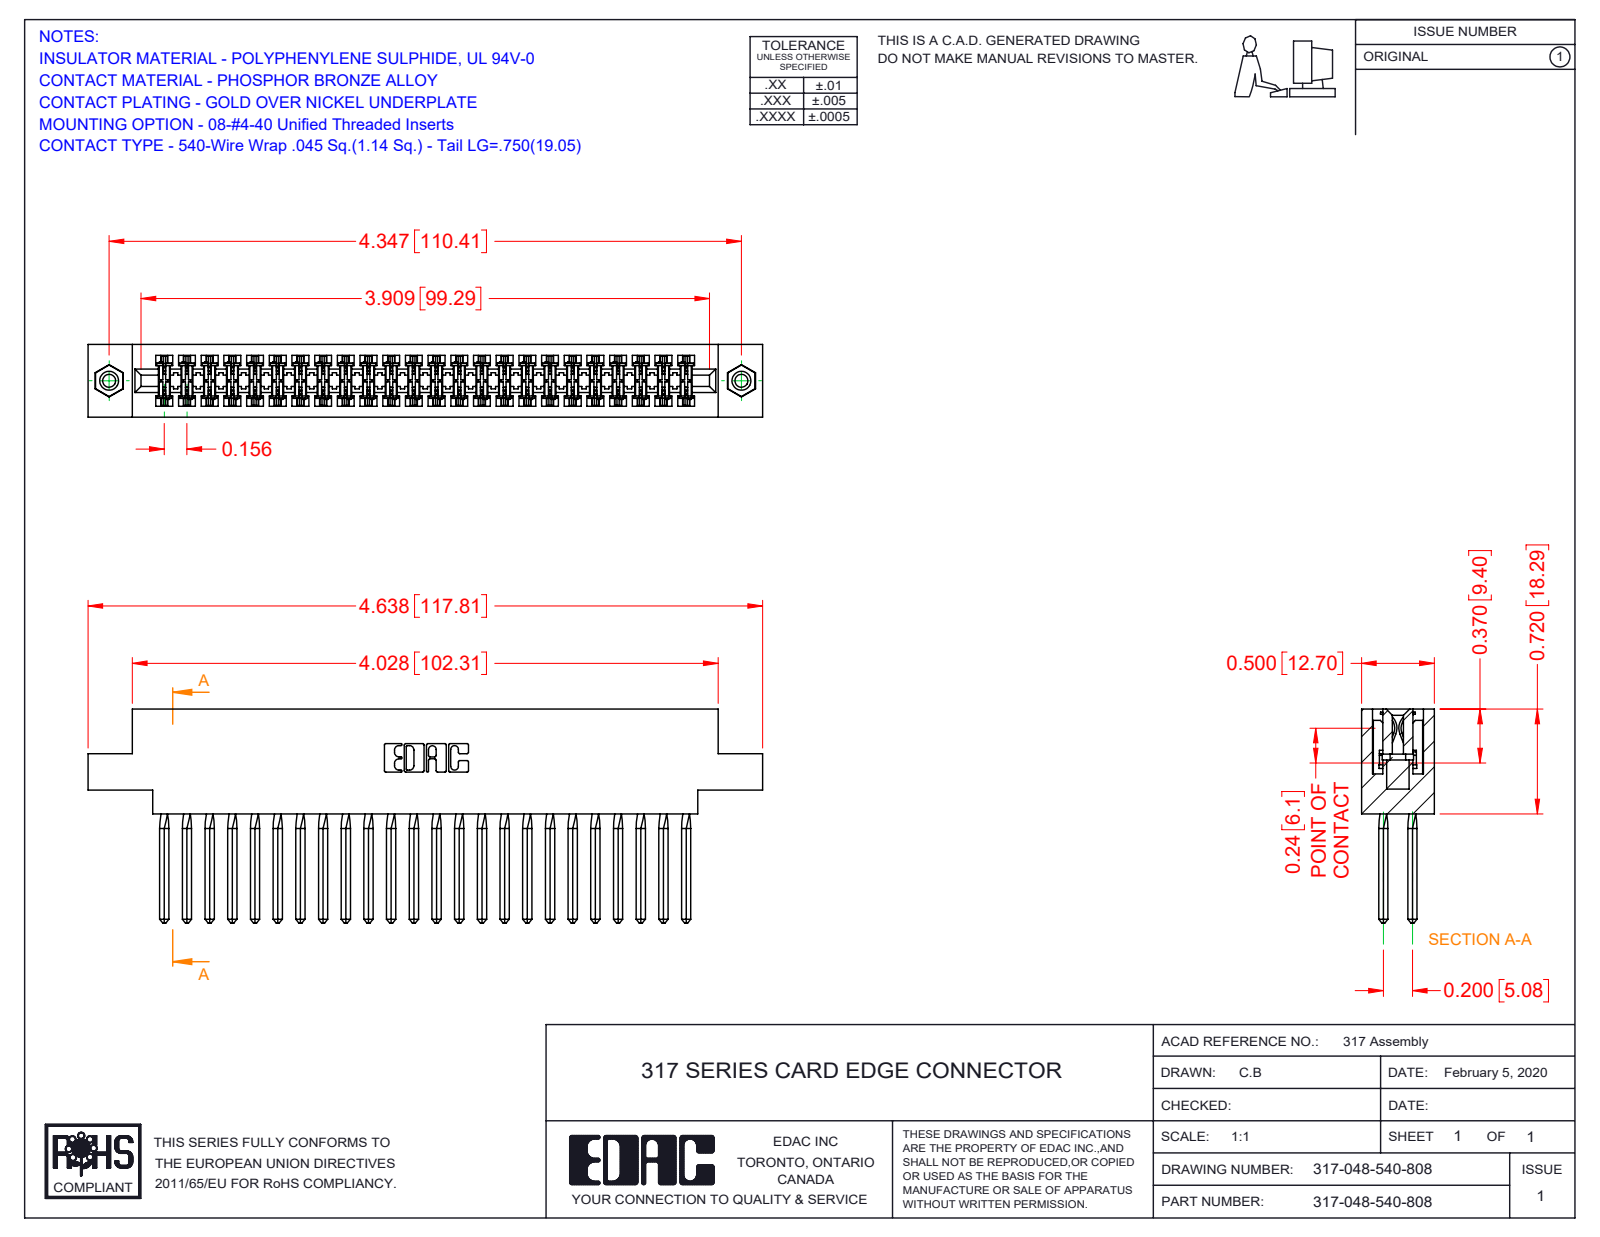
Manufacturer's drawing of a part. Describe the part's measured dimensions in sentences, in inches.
The part is named "317-290-001_540; 345-250-001_345-250-003-102; 317 Part_.156 Dia - TI; 317-048-540-878". Its 3-D file was written by "SolidWorks 2016 (CONFIG_CONTROL_DESIGN)". It is 51 solids with 4434 faces: 3594 planar, 632 cylindrical and 208 other. Overall it measures 4.638 by 1.47 by 0.5 inches. Its volume is 1.169 cubic inches and its surface area 43.25 square inches. Round holes: 2 of diameter 0.089, 2 of diameter 0.125, 2 of diameter 0.156. Round bosses or shafts: 2 of diameter 0.155. Partial cylindrical surfaces (rounded edges, fillets, slot ends): 96 of radius 0.015, 22 of radius 0.01, 6 of radius 0.007, 6 of radius 0.031, 3 of radius 0.026, 2 of radius 0.095, 2 of radius 0.1, 2 of radius 0.11. The main face-to-face distances are 0.5, 0.075, 0.425, 0.35, 0.11, 0.195, 0.094, 0.72, 0.2, 0.115. The hole center spacings are 4.347.
